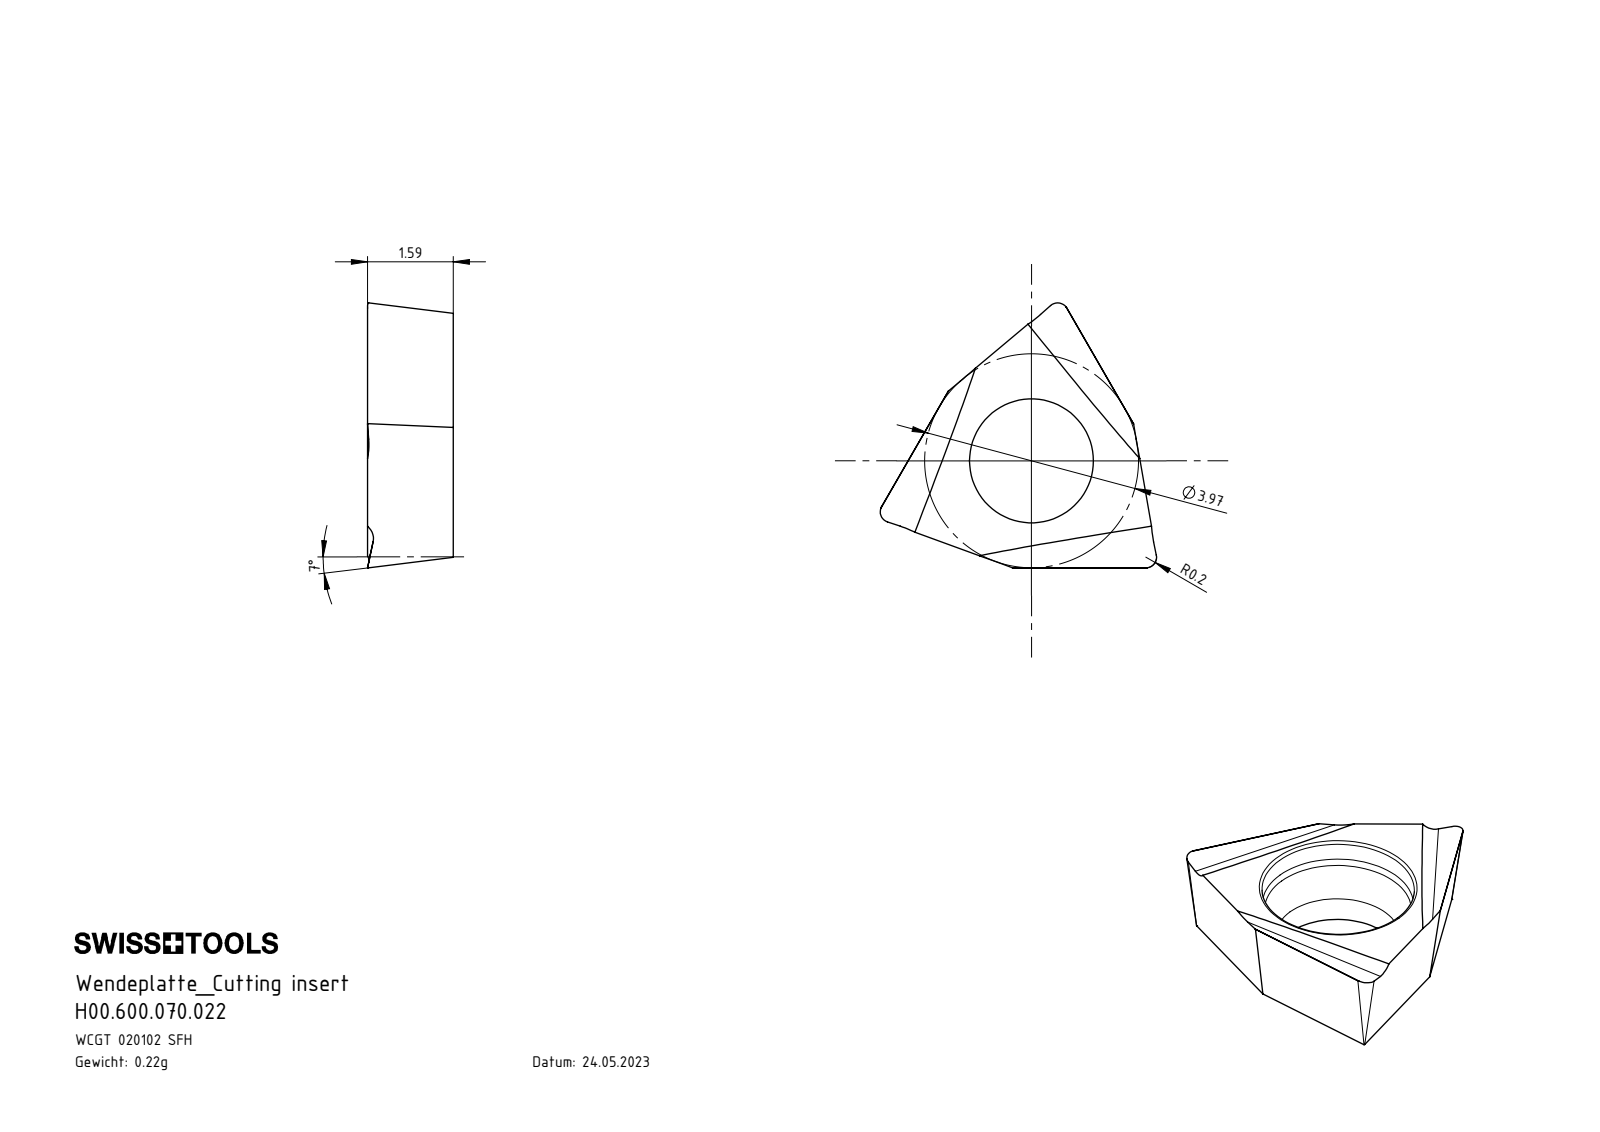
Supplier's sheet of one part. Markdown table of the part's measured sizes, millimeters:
| quantity | value |
| --- | --- |
| part name | H00.600.070.022 |
| STEP written by | SolidWorks 2022 (AUTOMOTIVE_DESIGN) |
| units | millimeters |
| bodies | 1 solid, 31 faces (14 planar, 5 cylindrical, 12 other) |
| overall size | 5.13 × 4.92 × 1.59 |
| volume | 15 mm³ |
| surface area | 56 mm² |
| round holes (diameter × count) | 2.3 × 1 |
| partial cylindrical surfaces (radius × count) | 0.3 × 3 |
| main face-to-face distances | 1.59 |
